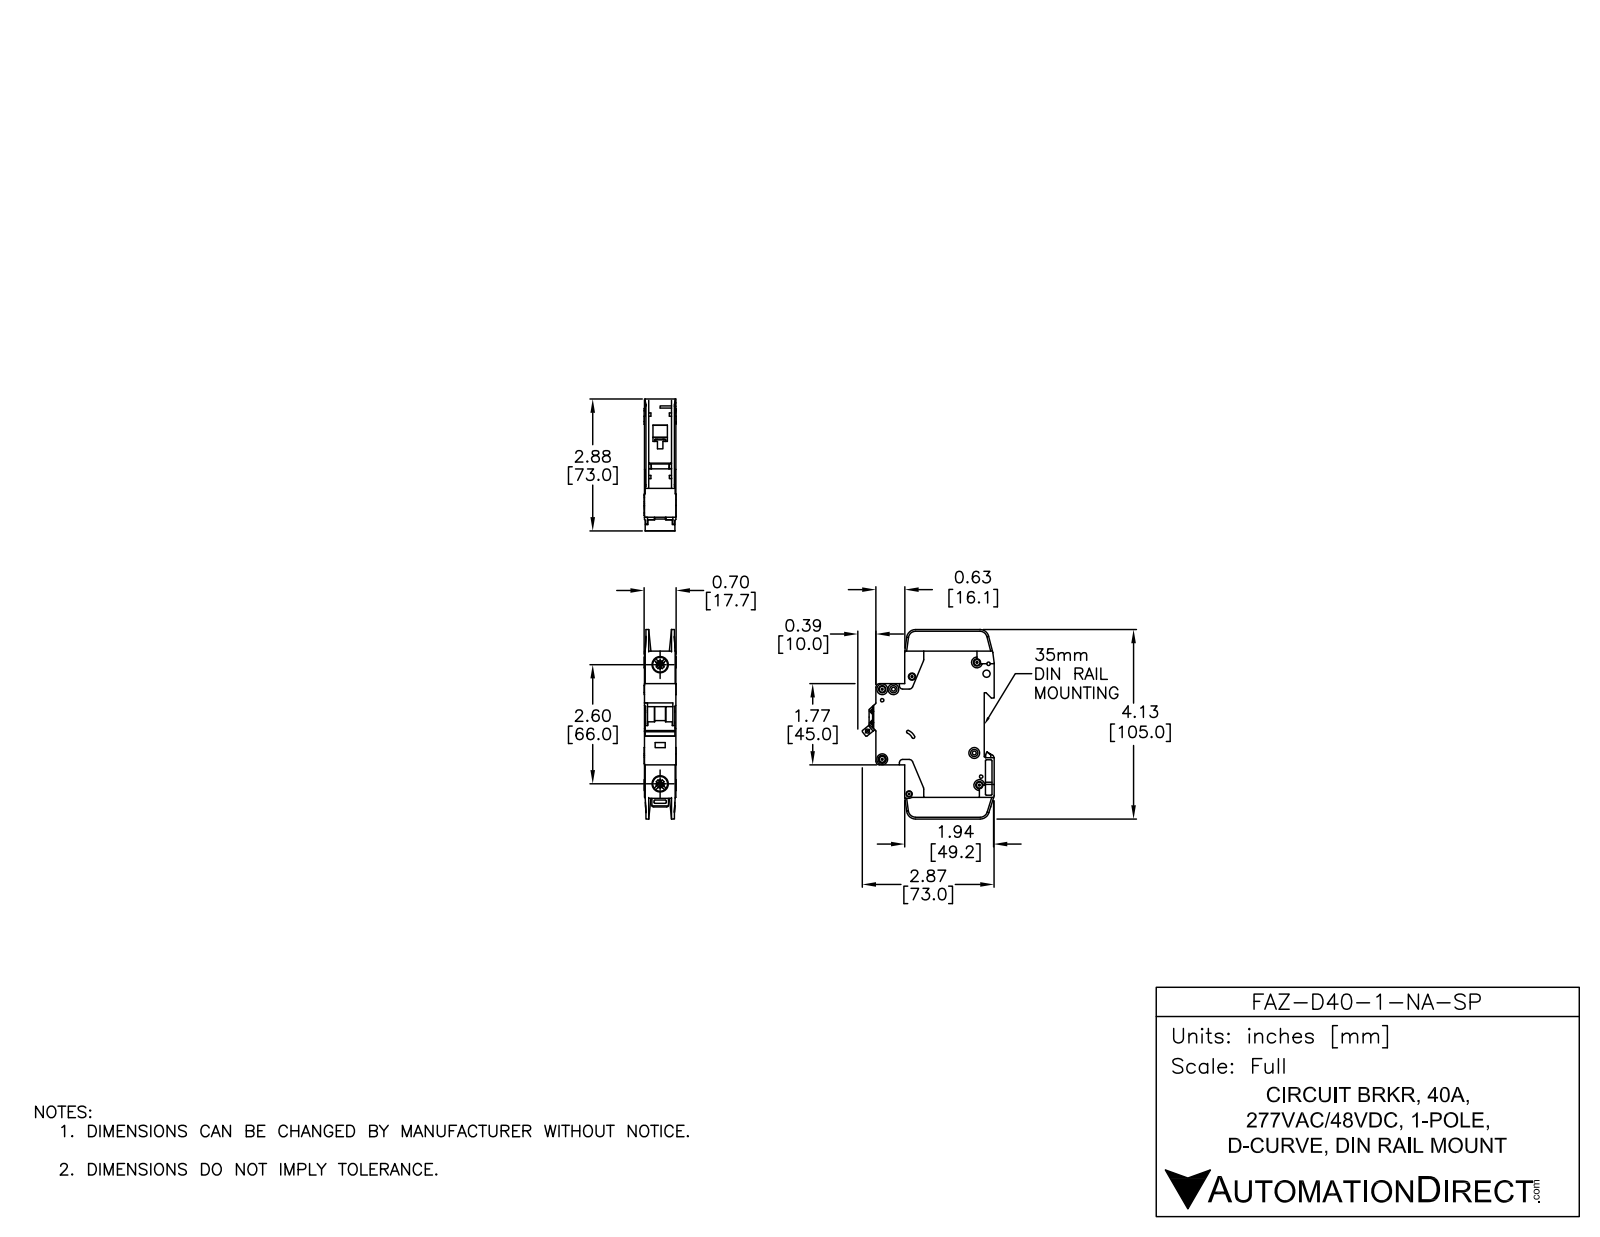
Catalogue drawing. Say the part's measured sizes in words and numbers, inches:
The part is named "FAZ-D40-1-NA-SP". Its 3-D file was written by "SolidWorks 2014 (AUTOMOTIVE_DESIGN)". It is 3 solids with 784 faces: 409 planar, 263 cylindrical and 112 other. Overall it measures 4.134 by 2.876 by 0.697 inches. Its volume is 4.741 cubic inches and its surface area 38.35 square inches. Round holes: 7 of diameter 0.142, 2 of diameter 0.043, 2 of diameter 0.059, 2 of diameter 0.157, 2 of diameter 0.281, 2 of diameter 0.323, 1 of diameter 0.075, 1 of diameter 0.085, 1 of diameter 0.087, 1 of diameter 0.1, 1 of diameter 0.13, 1 of diameter 0.134. Round bosses or shafts: 7 of diameter 0.236, 1 of diameter 0.098. Partial cylindrical surfaces (rounded edges, fillets, slot ends): 29 of radius 0.01, 18 of radius 0.02, 10 of radius 0.039, 10 of radius 0.079, 5 of radius 0.197, 4 of radius 0.157, 3 of radius 0.071, 2 of radius 0.008. The main face-to-face distances are 0.689, 0.593, 0.028, 0.096, 0.069, 0.62, 0.524, 0.551, 0.496, 0.079. The hole center spacings are 0.244, 0.204, 0.24, 0.322, 0.337, 0.343, 0.437, 0.49.
